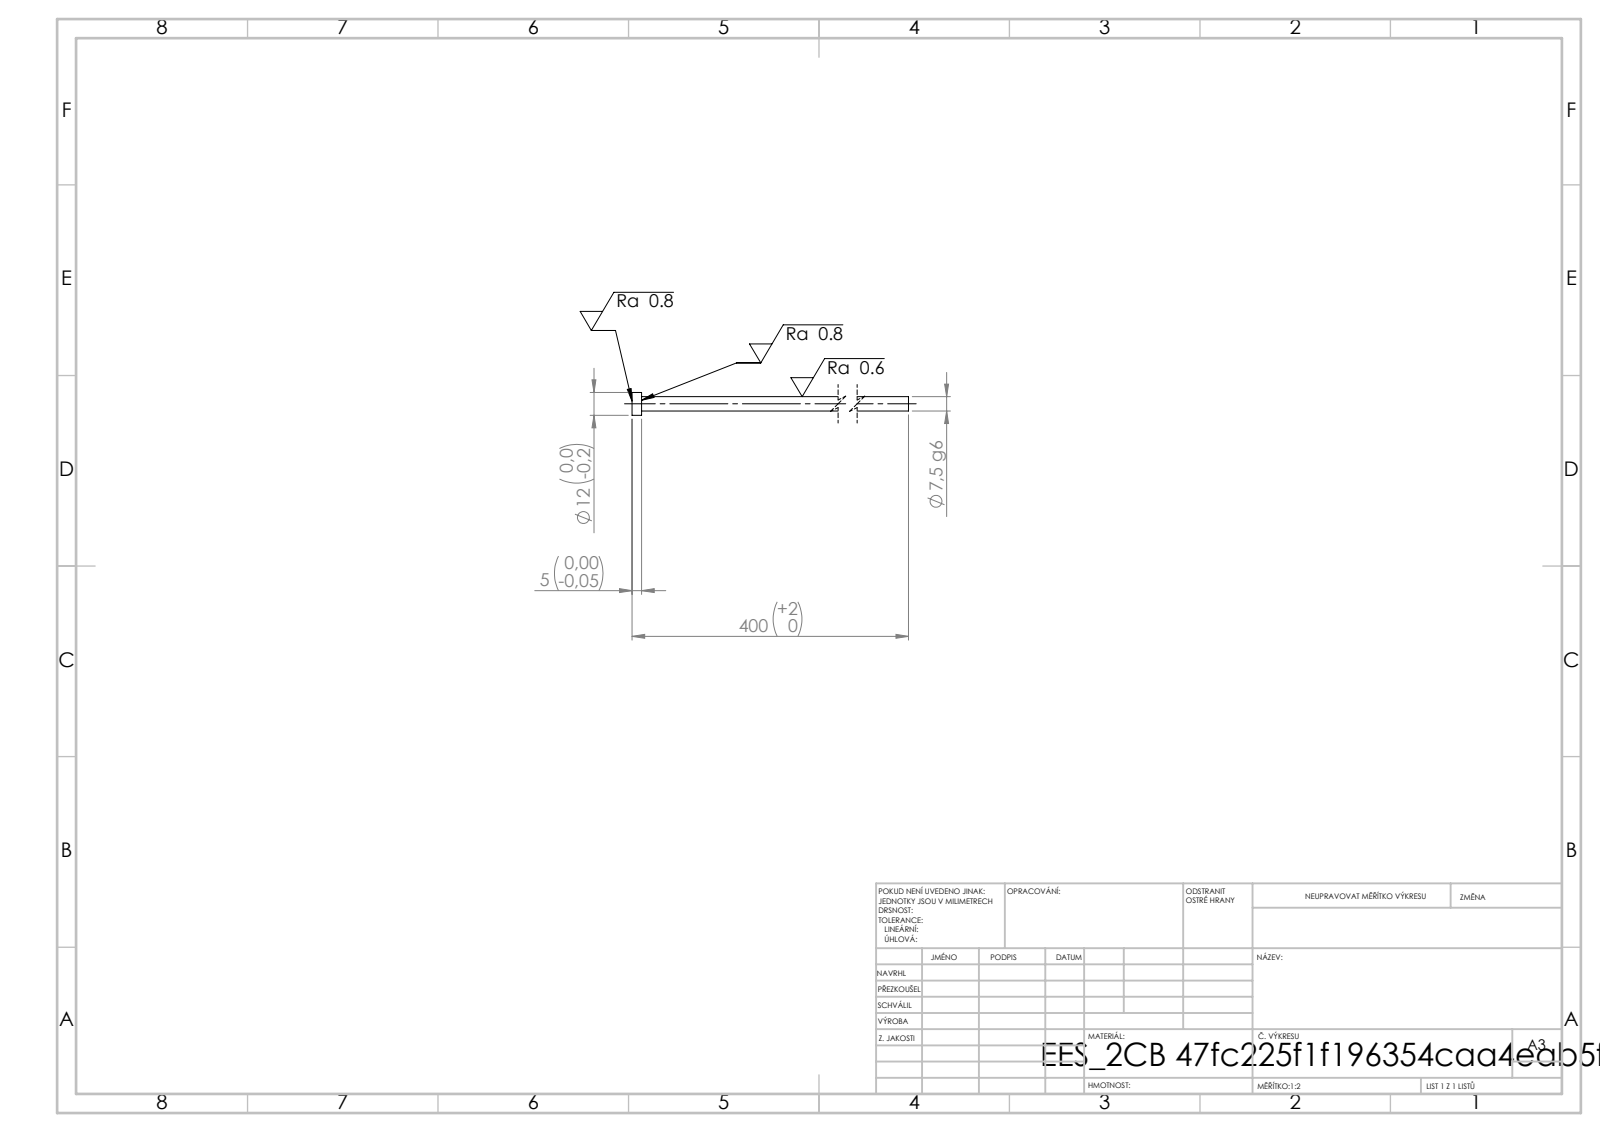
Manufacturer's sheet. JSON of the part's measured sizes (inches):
{"step_written_by": "SolidWorks 2019 (CONFIG_CONTROL_DESIGN)", "units": "inches", "bodies": {"solids": 1, "faces": 7, "planar": 3, "cylindrical": 4, "other": 0}, "overall_size": [15.748, 0.472, 0.472], "volume_in3": 1.099, "surface_area_in2": 15.07, "round_bosses_or_shafts": [[0.472, 1], [0.295, 1]], "face_to_face_distances": [0.197, 15.748, 15.551]}
